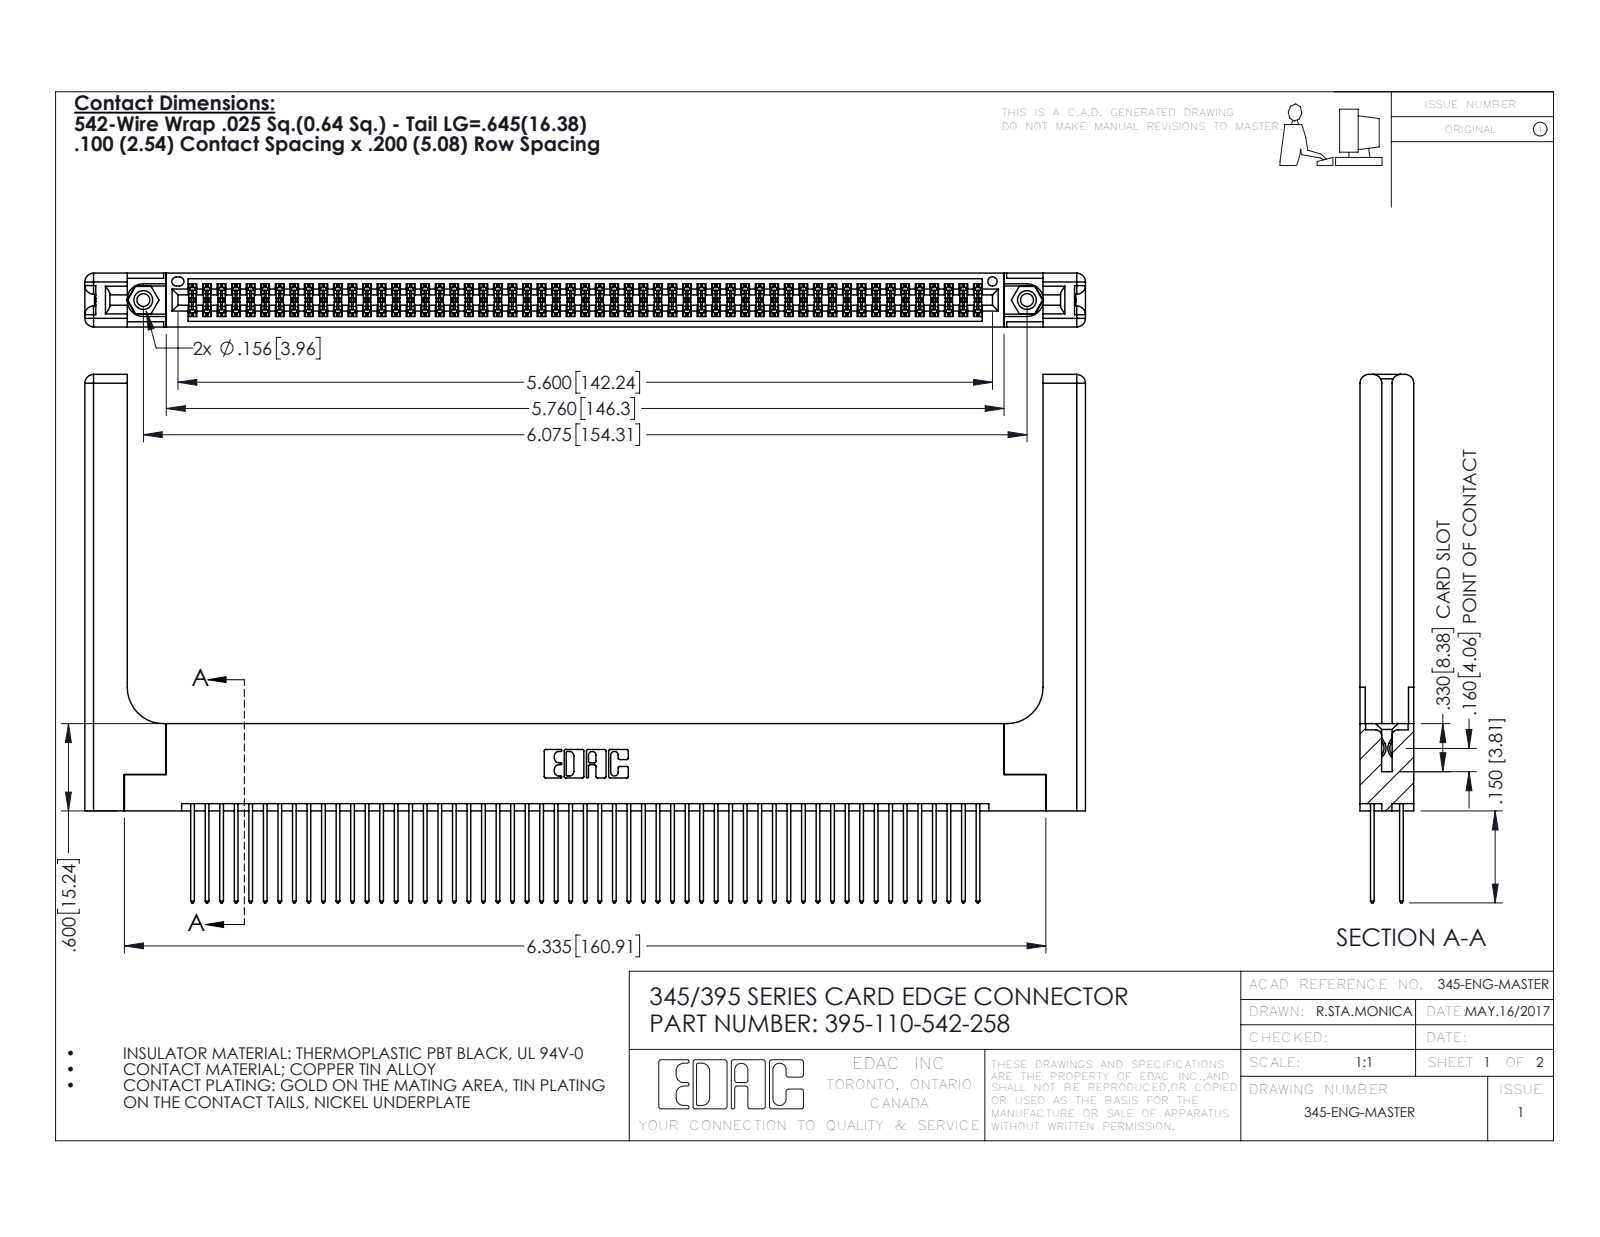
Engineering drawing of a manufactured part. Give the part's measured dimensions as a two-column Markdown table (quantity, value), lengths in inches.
| quantity | value |
| --- | --- |
| part name | 345-292-001_345-293-142; 345-250-001_345-250-001-102; 345 Part_Flush Mounting Lugs - 0.156 Dia-TH; 395-110-542-258 (+1 more) |
| STEP written by | SolidWorks 2016 (CONFIG_CONTROL_DESIGN) |
| units | inches |
| bodies | 115 solids, 5882 faces (3858 planar, 1964 cylindrical, 60 other) |
| overall size | 6.879 × 3.632 × 0.37 |
| volume | 1.592 in³ |
| surface area | 52.29 in² |
| round holes (diameter × count) | 0.089 × 2, 0.125 × 2, 0.156 × 2, 0.064 × 1 |
| round bosses / shafts (diameter × count) | 0.155 × 2 |
| partial cylindrical surfaces (radius × count) | 0.006 × 165, 0.01 × 110, 0.01 × 22, 0.06 × 16, 0.007 × 6, 0.031 × 6, 0.026 × 3, 0.014 × 2 |
| main face-to-face distances | 0.072, 0.298, 0.2, 0.37, 0.098, 0.272, 0.025, 0.225, 0.175, 0.148 |
| hole center spacings | 0.27, 5.839, 6.075 |
